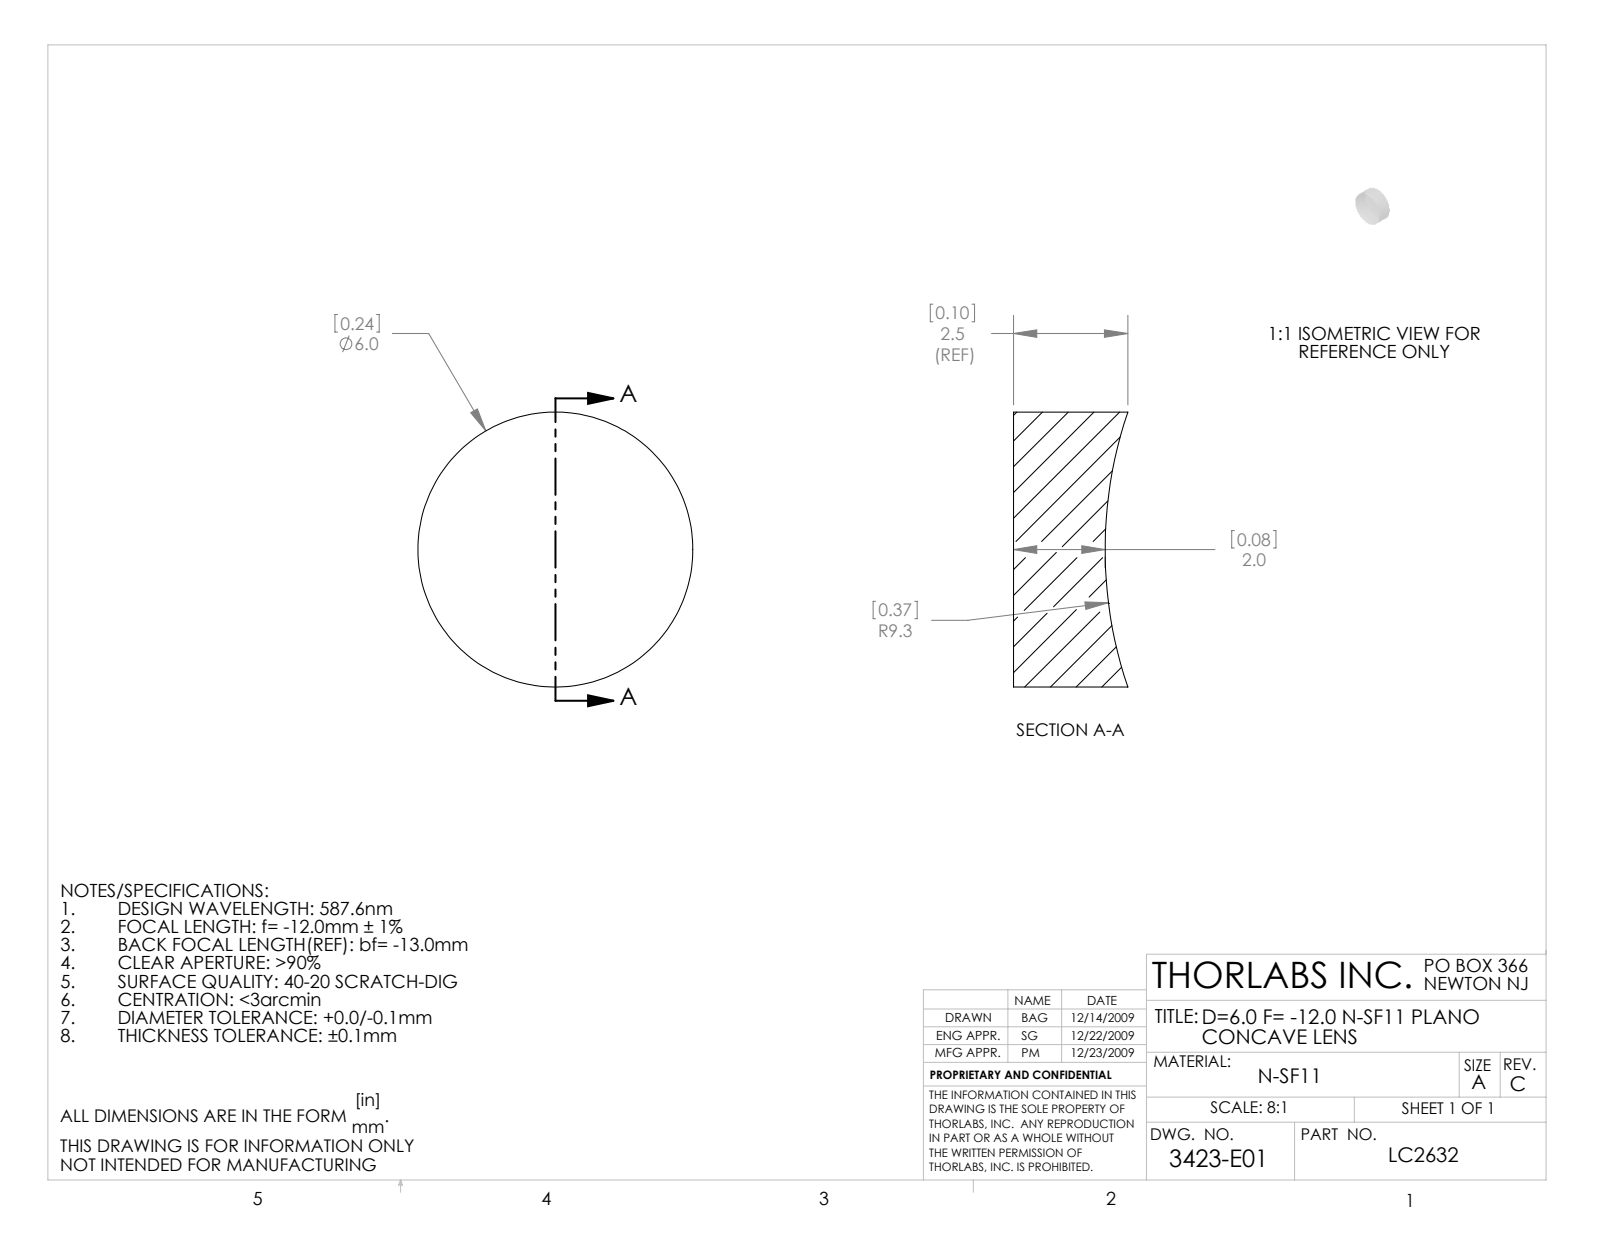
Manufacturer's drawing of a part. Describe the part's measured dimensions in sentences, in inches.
The part is named "3423-E0W". Its 3-D file was written by "SolidWorks 2009 (AUTOMOTIVE_DESIGN)". It is 1 solid with 5 faces: 1 planar, 2 cylindrical and 2 other. Overall it measures 0.236 by 0.236 by 0.098 inches. Its volume is 0.004 cubic inches and its surface area 0.162 square inches. Round bosses or shafts: 1 of diameter 0.236.
